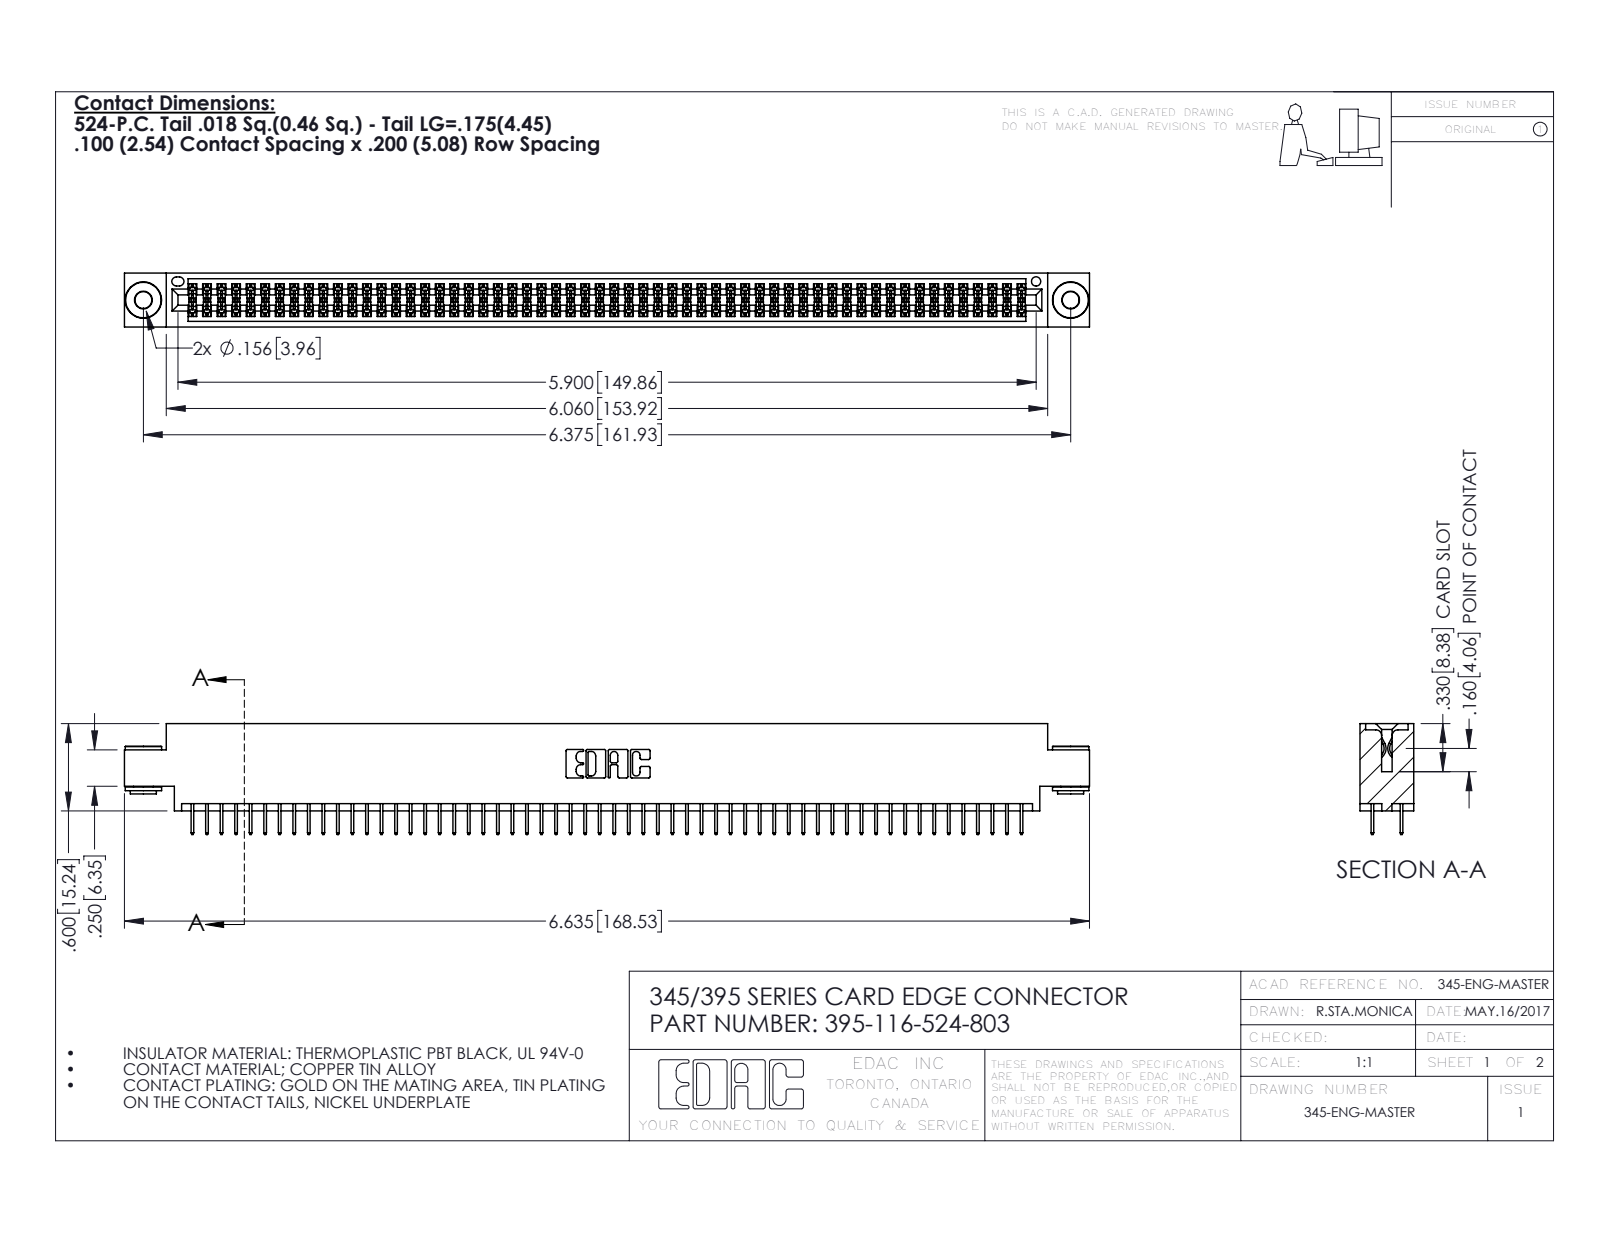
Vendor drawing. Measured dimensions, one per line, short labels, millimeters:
name: 345-292-001_345-293-124; 395-116-524-803; 345 Part_0.170 Offset - 0.156 Dia-TH; 345-250-002_345-250-002-102
written by: SolidWorks 2016 (CONFIG_CONTROL_DESIGN)
unit: mm
bodies: 119 solids, 6432 faces (4618 planar, 1806 cylindrical, 8 other)
size: 168.5 × 19.4 × 9.4
volume: 16 300 mm³; area: 24 210 mm²
holes: 2× ⌀2.9, 2× ⌀4, 1× ⌀1.6
bosses: 2× ⌀6.4, 2× ⌀4.6, 2× ⌀3.5
rounds: 174× R0.2, 22× R0.3, 6× R0.2, 6× R0.8, 3× R0.7, 2× R0.4, 2× R0.5, 2× R0.6
face distances: 1.8, 7.6, 9.4, 5.1, 2.5, 6.9, 0.6, 5.7, 4.4, 1.8
hole spacings: 6.9, 155.9, 161.9
